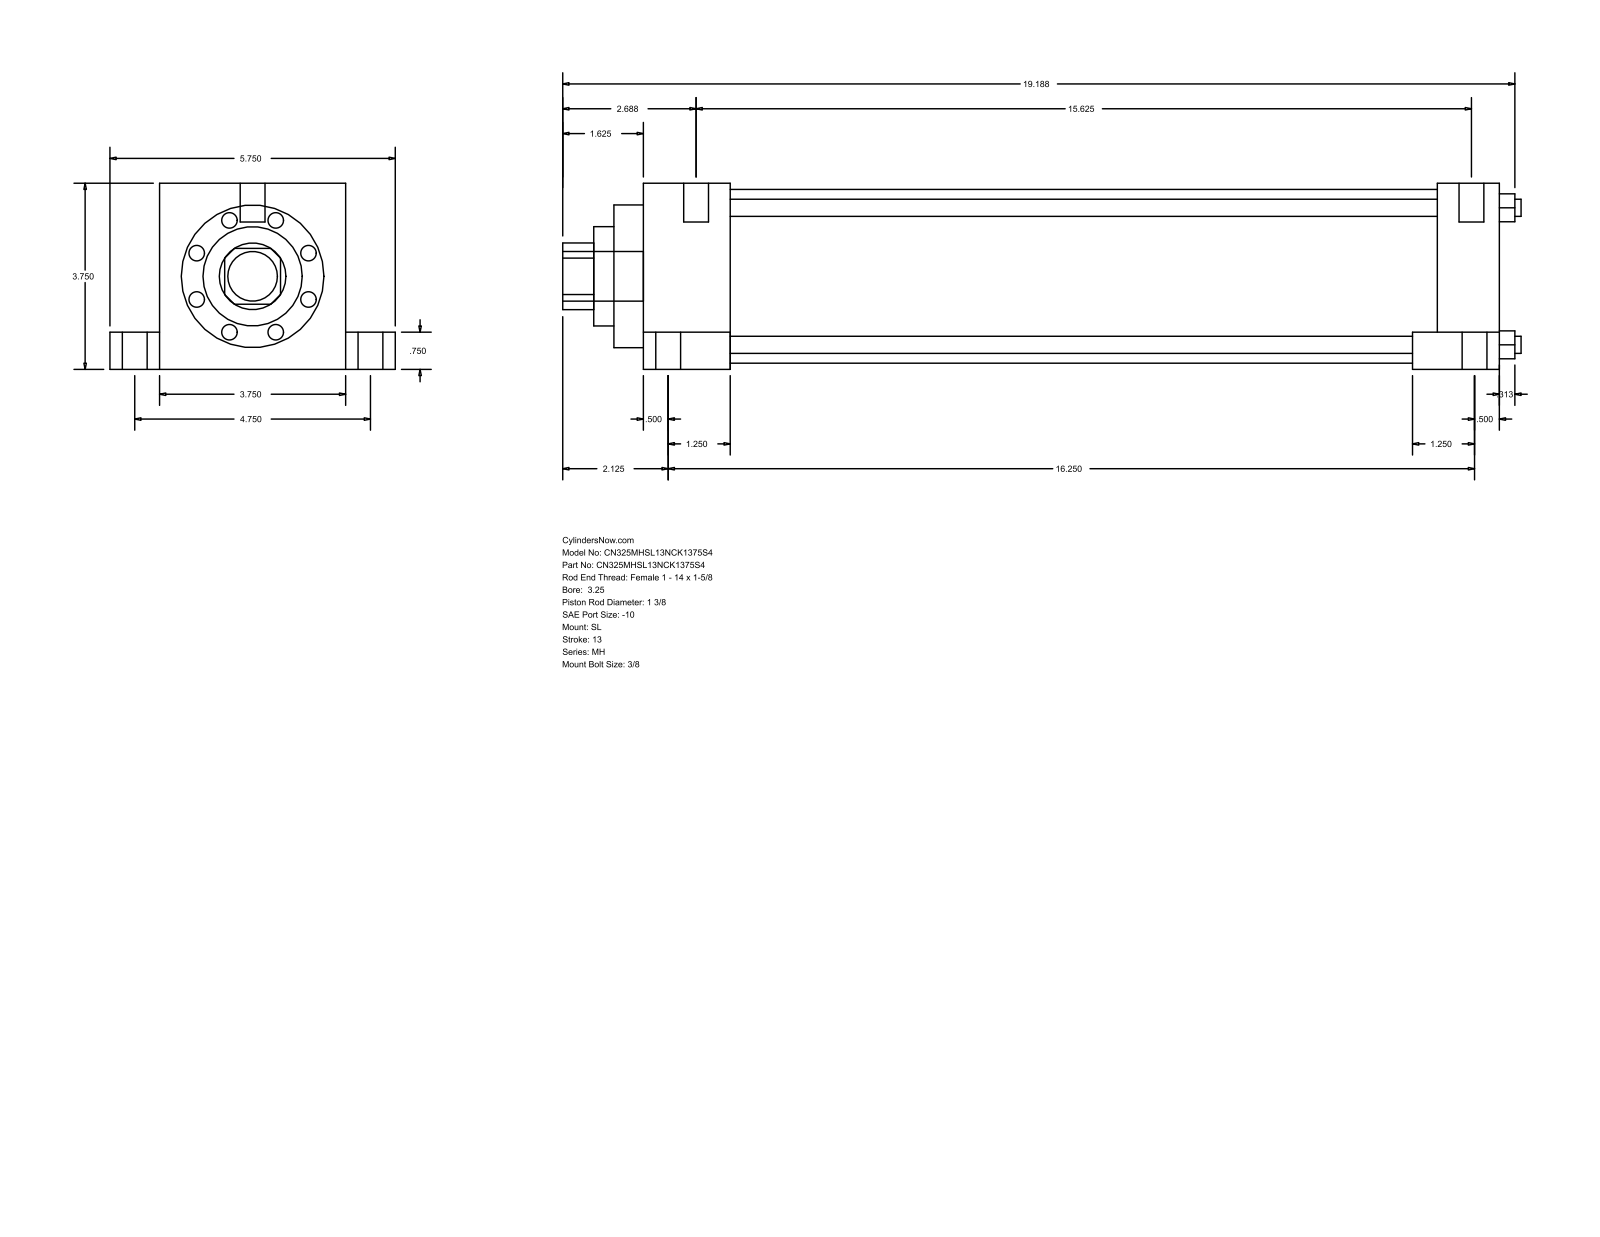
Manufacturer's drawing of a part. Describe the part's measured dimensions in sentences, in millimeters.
The part is named "MH_SL__0325_1.375". Its 3-D file was written by "GSSL Pune (CONFIG_CONTROL_DESIGN)". It is 0 solids with 110 faces: 77 planar, 33 cylindrical and 0 other. Overall it measures 490.54 by 146.05 by 95.25 millimeters. Round holes: 4 of diameter 8.76, 1 of diameter 34.92, 1 of diameter 50.8, 1 of diameter 73.03, 1 of diameter 88.9. Round bosses or shafts: 6 of diameter 12.7, 4 of diameter 19.05, 4 of diameter 5.56, 1 of diameter 25.4. Partial cylindrical surfaces (rounded edges, fillets, slot ends): 1 of radius 17.06. The main face-to-face distances are 95.24, 438.16, 44.45, 393.71, 25.41, 120.65, 19.05, 76.19, 406.41, 361.96. The hole center spacings are 49.57, 70.1, 99.14.
